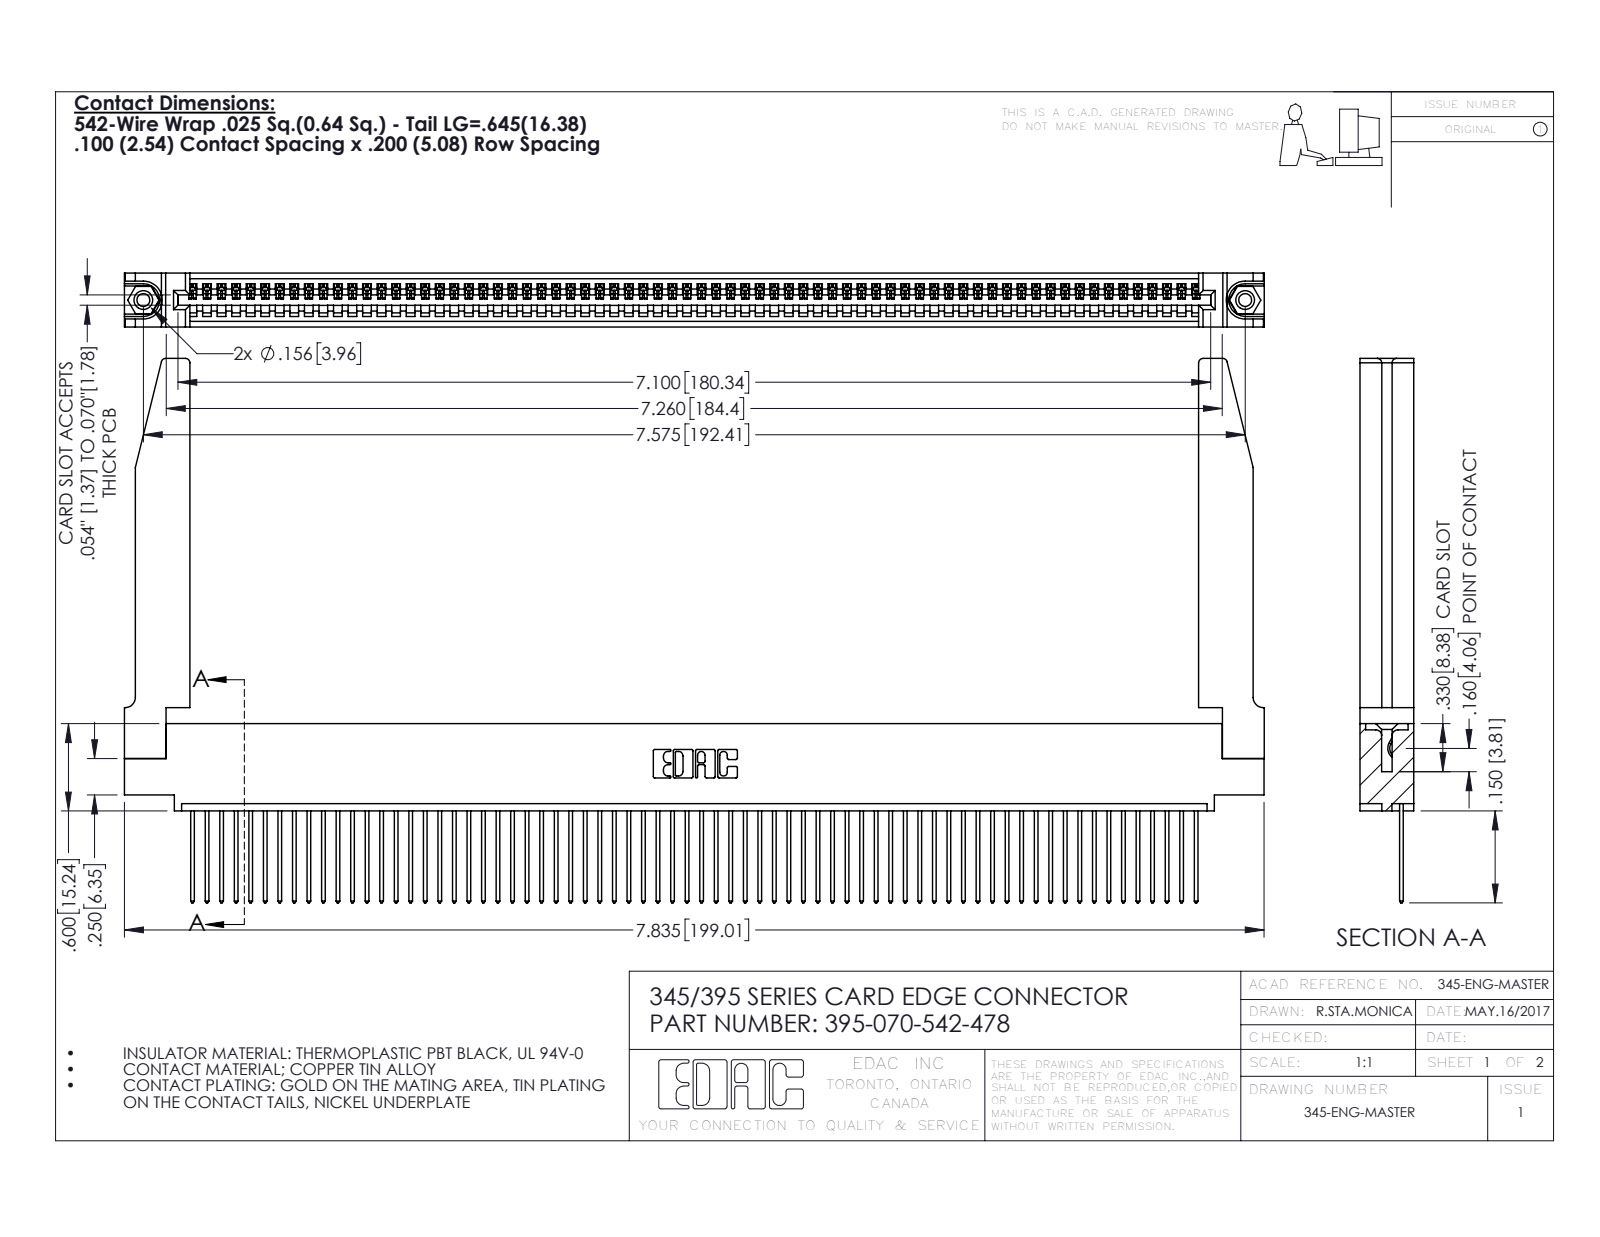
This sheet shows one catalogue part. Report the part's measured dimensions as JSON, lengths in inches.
{"part_name": "345-220-078_345-220-078; 345 Part_0.110 Offset - 0.156 Dia-TH; 345-250-001_345-250-001-102; 395-070-542-478 (+1 more)", "step_written_by": "SolidWorks 2016 (CONFIG_CONTROL_DESIGN)", "units": "inches", "bodies": {"solids": 75, "faces": 4424, "planar": 3026, "cylindrical": 1346, "other": 52}, "overall_size": [7.836, 3.742, 0.37], "volume_in3": 1.647, "surface_area_in2": 52.44, "round_holes": [[0.089, 2], [0.125, 2], [0.156, 2], [0.064, 1]], "round_bosses_or_shafts": [[0.155, 2]], "partial_cylinders_radius": [[0.006, 140], [0.01, 140], [0.01, 22], [0.03, 8], [0.007, 6], [0.031, 6], [0.026, 3], [0.031, 2]], "face_to_face_distances": [0.072, 0.298, 0.37, 0.098, 0.272, 0.025, 0.2, 0.225, 0.149, 0.148], "hole_center_spacings": [0.27, 7.339, 7.575]}
